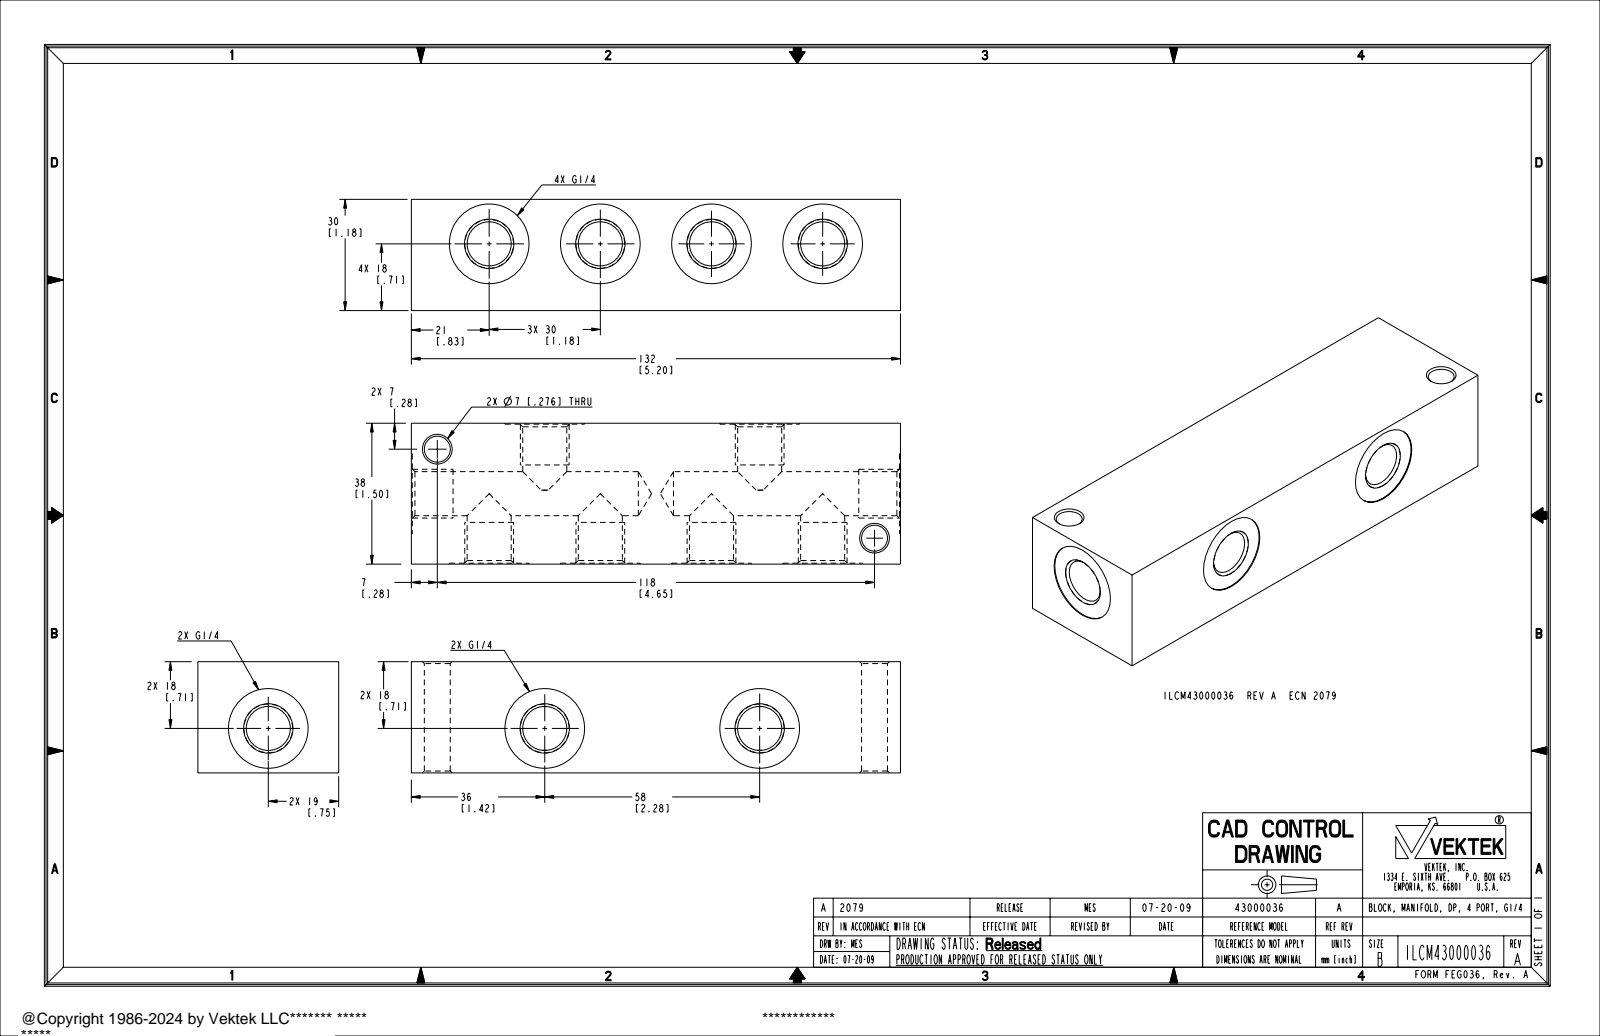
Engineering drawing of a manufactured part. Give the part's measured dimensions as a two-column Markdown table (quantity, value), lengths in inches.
| quantity | value |
| --- | --- |
| part name | ILCM43000036 |
| STEP written by | PRO/ENGINEER BY PARAMETRIC TECHNOLOGY CORPORATION, 2007460 (AUTOMOTIVE_DESIGN_CC2) |
| units | inches |
| bodies | 1 solid, 114 faces (22 planar, 60 cylindrical, 32 other) |
| overall size | 5.197 × 1.496 × 1.181 |
| volume | 7.592 in³ |
| surface area | 49.07 in² |
| round holes (diameter × count) | 0.468 × 7, 0.846 × 7, 0.276 × 2 |
| round bosses / shafts (diameter × count) | 0.518 × 7 |
| main face-to-face distances | 1.181, 1.496, 1.486, 5.197, 1.476, 5.187, 5.177, 0.443, 0.433, 1.053 |
| hole center spacings | 1.181, 0.591, 2.362, 0.512, 0.669, 1.693, 1.772, 2.283 |
